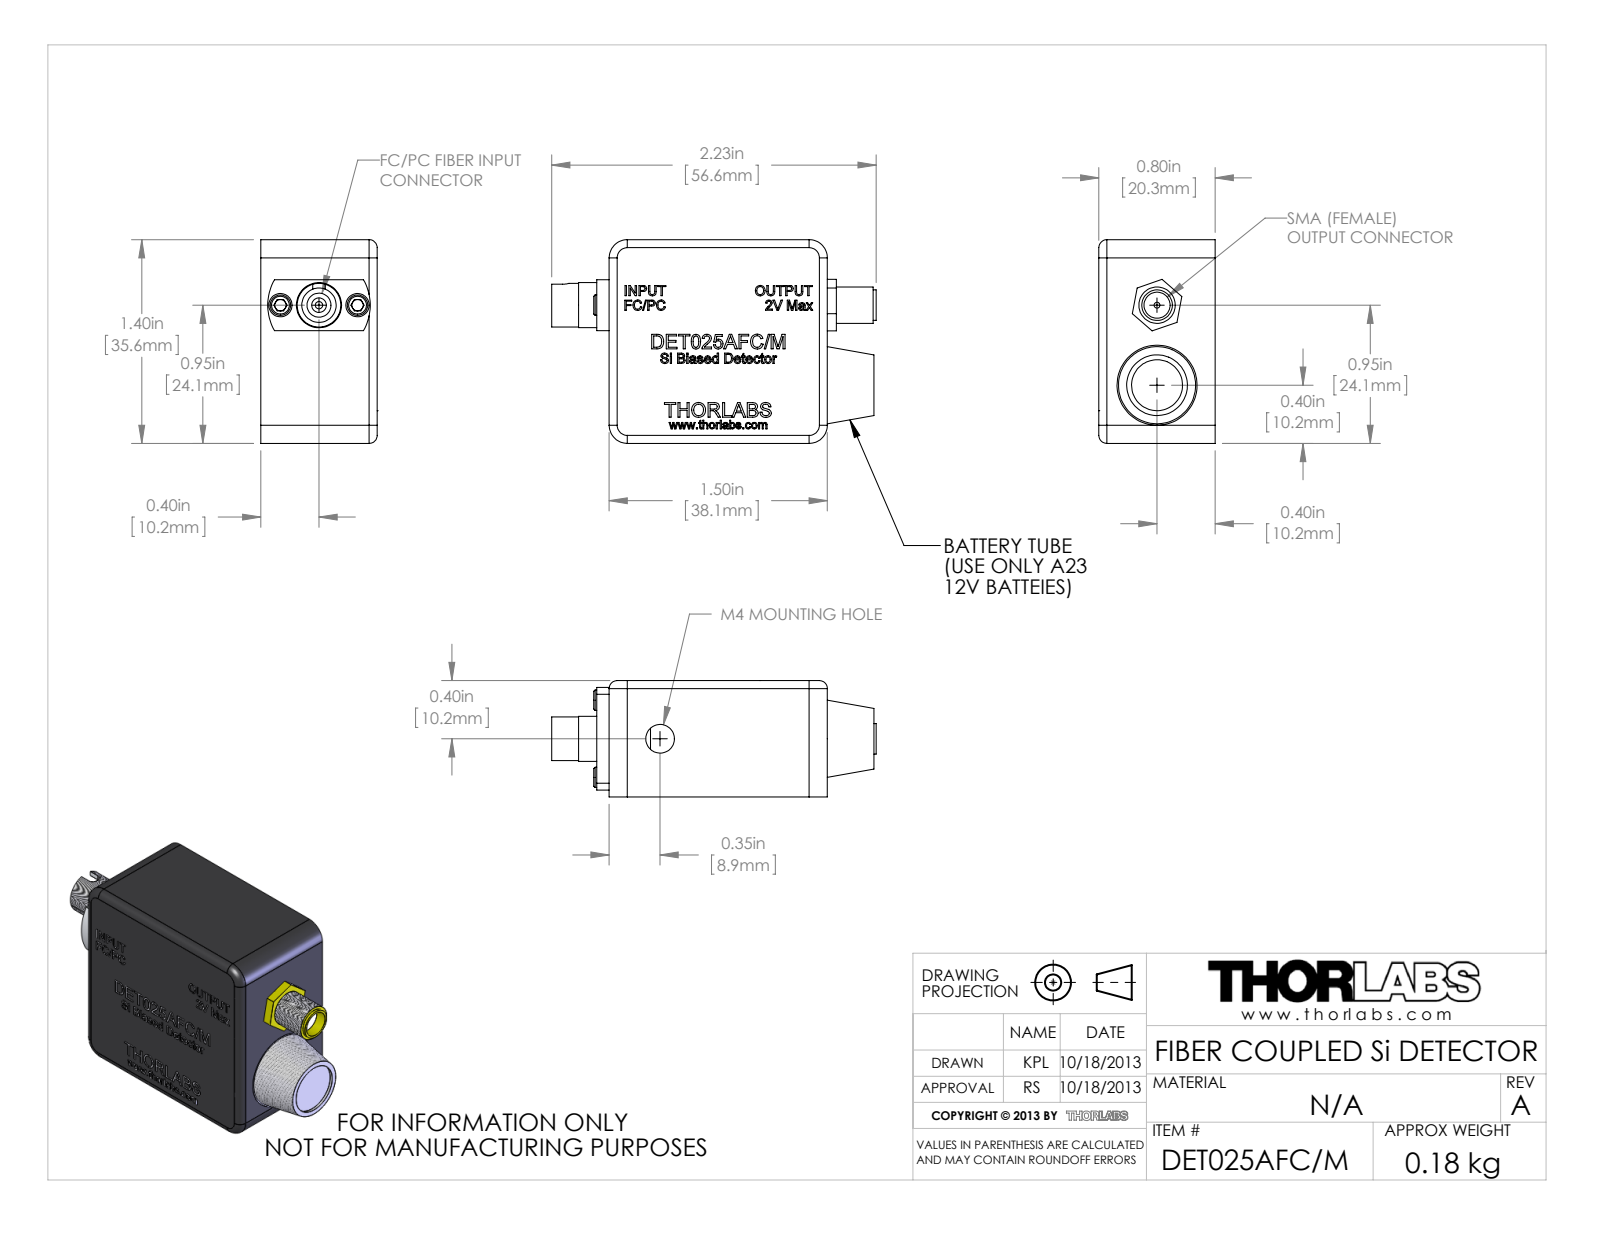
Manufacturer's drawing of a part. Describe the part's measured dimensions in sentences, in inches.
The part is named "TTN020177; socket head cap screw_ai_HX-SHCS 0.086-56x0.188x0.188-N; flat head screw_ai_CR-FHMS 0.086-56x0.188x0.188-N; SMA Edge Mount Adapter (+5 more)". Its 3-D file was written by "SolidWorks 2012 (AUTOMOTIVE_DESIGN)". It is 12 solids with 1726 faces: 1037 planar, 178 cylindrical and 511 other. Overall it measures 2.23 by 1.4 by 0.8 inches. Its volume is 1.071 cubic inches and its surface area 21.75 square inches. Round holes: 6 of diameter 0.07, 4 of diameter 0.096, 4 of diameter 0.14, 3 of diameter 0.125, 2 of diameter 0.085, 2 of diameter 0.16, 1 of diameter 0.017, 1 of diameter 0.04, 1 of diameter 0.05, 1 of diameter 0.05, 1 of diameter 0.1, 1 of diameter 0.125. Round bosses or shafts: 6 of diameter 0.086, 4 of diameter 0.147, 2 of diameter 0.14, 1 of diameter 0.472, 1 of diameter 0.432, 1 of diameter 0.327, 1 of diameter 0.31, 1 of diameter 0.3. Partial cylindrical surfaces (rounded edges, fillets, slot ends): 12 of radius 0.125, 4 of radius 0.032, 4 of radius 0.055, 4 of radius 0.08, 4 of radius 0.095, 2 of radius 0.06, 2 of radius 0.1, 1 of radius 0.008. The main face-to-face distances are 0.063, 0.737, 0.8, 1.4, 0.5, 0.563, 0.237, 0.1, 1.5, 1.3. The hole center spacings are 1.698, 1.15, 1.25, 1.25, 1.15, 0.265, 0.377, 0.611.
